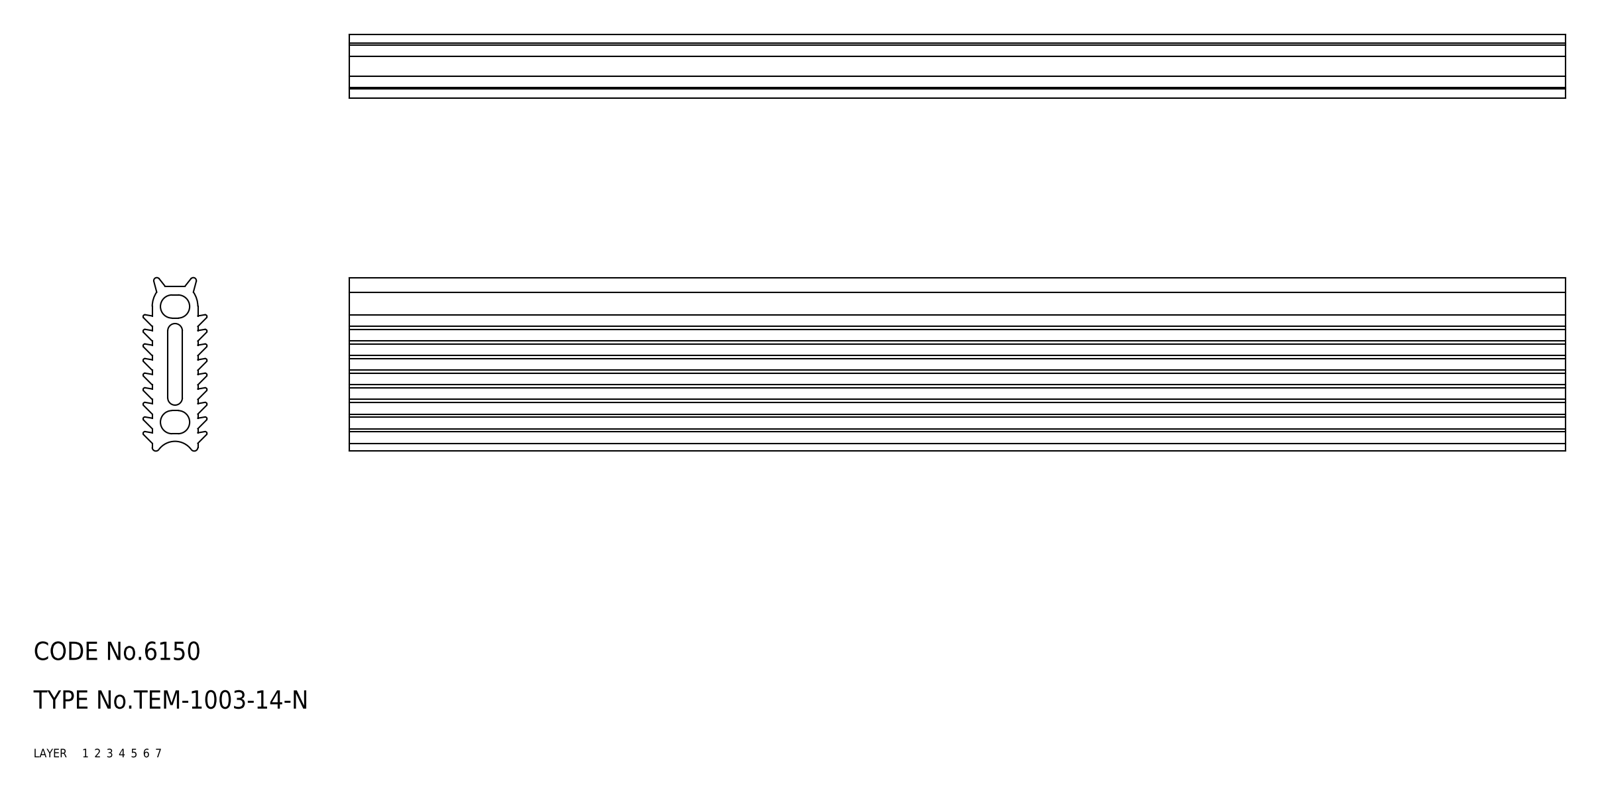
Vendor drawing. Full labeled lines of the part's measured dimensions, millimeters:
Part name (STEP PRODUCT): gasket
STEP written by: CADfix (AUTOMOTIVE_DESIGN)
Units: millimetres
Bodies: 1 solid, 100 faces (0 planar, 0 cylindrical, 100 other)
Overall size (bounding box): 200 × 28.5 × 10.5
Volume: 33 136 mm³ · Surface area: 34 382 mm²
